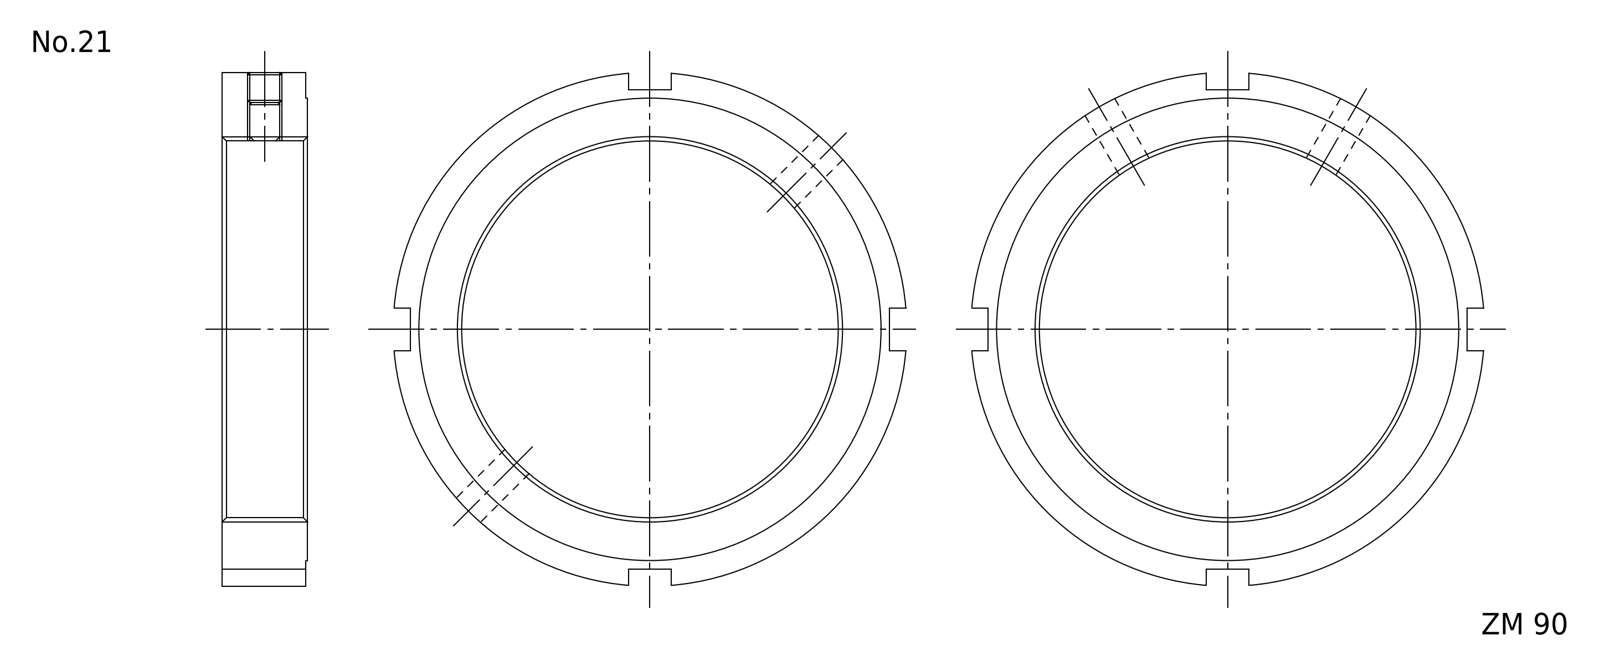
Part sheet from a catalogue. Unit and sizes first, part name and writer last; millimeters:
Units: millimetres
Overall size (bounding box): 119.58 × 119.58 × 20
Round holes (diameter × count): ⌀6.65 ×2, ⌀90 ×1
Round bosses / shafts (diameter × count): ⌀120 ×1, ⌀108 ×1
Main face-to-face distances: 20, 0.5, 19.5, 51, 61, 112, 10
Volume: 93 779 mm³ · Surface area: 23 836 mm²
Bodies: 1 solid, 23 faces (15 planar, 8 cylindrical, 0 other)
Part name (STEP PRODUCT): FKD ZM 90
STEP written by: Autodesk Inventor 2011 (AUTOMOTIVE_DESIGN)
